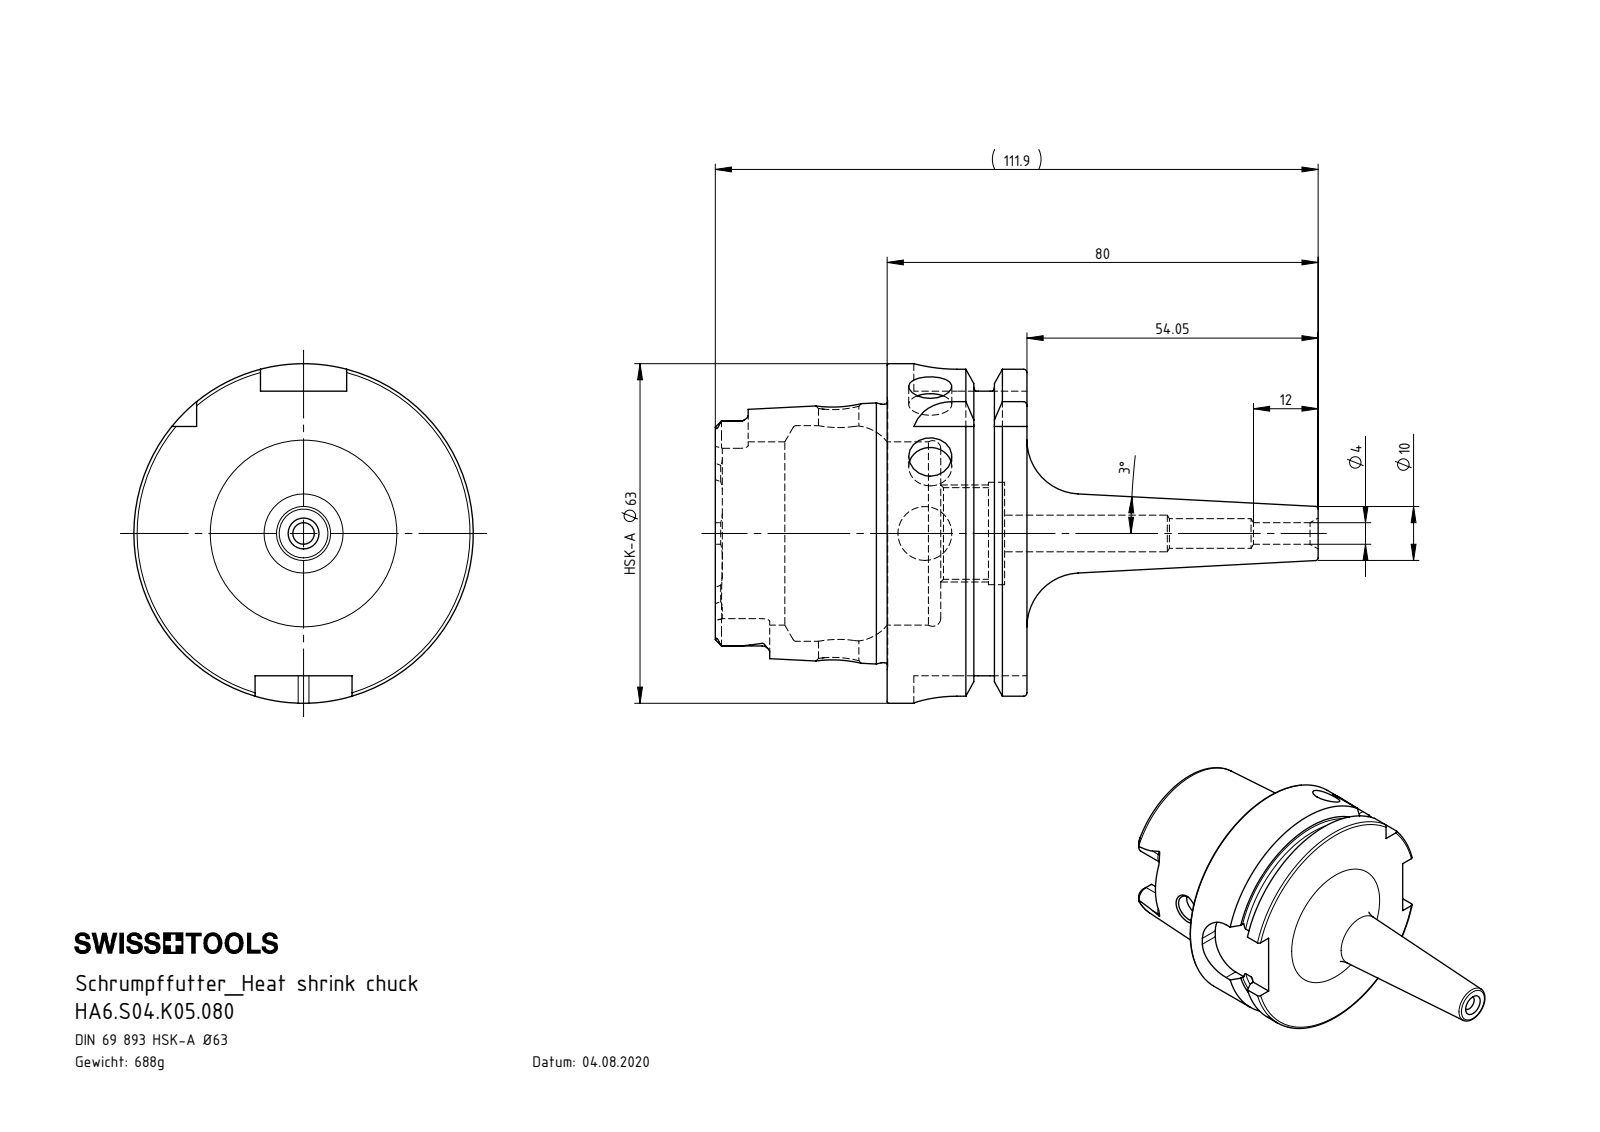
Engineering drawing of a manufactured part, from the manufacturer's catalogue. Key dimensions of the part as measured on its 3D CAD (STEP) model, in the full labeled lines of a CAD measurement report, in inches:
Part name (STEP PRODUCT): HA6.S04.K05.080
STEP written by: SolidWorks 2017 (AUTOMOTIVE_DESIGN)
Units: inches
Bodies: 1 solid, 139 faces (48 planar, 34 cylindrical, 57 other)
Overall size (bounding box): 4.406 × 2.48 × 2.48
Volume: 5.354 in³ · Surface area: 39.31 in²
Round holes (diameter × count): ⌀0.315 ×2, ⌀0.157 ×1, ⌀0.217 ×1, ⌀0.268 ×1, ⌀0.295 ×1, ⌀0.394 ×1, ⌀0.669 ×1, ⌀0.748 ×1, ⌀1.339 ×1, ⌀1.575 ×1
Round bosses / shafts (diameter × count): ⌀2.48 ×1, ⌀2.163 ×1, ⌀1.887 ×1
Partial cylindrical surfaces — rounded edges, fillets, slot ends (radius × count): R0.055 ×6, R0.113 ×4, R0.315 ×4
Main face-to-face distances: 1.022, 0.63, 0.392, 1.256, 1.648, 2.278, 0.858, 2.079, 0.467, 2.114
